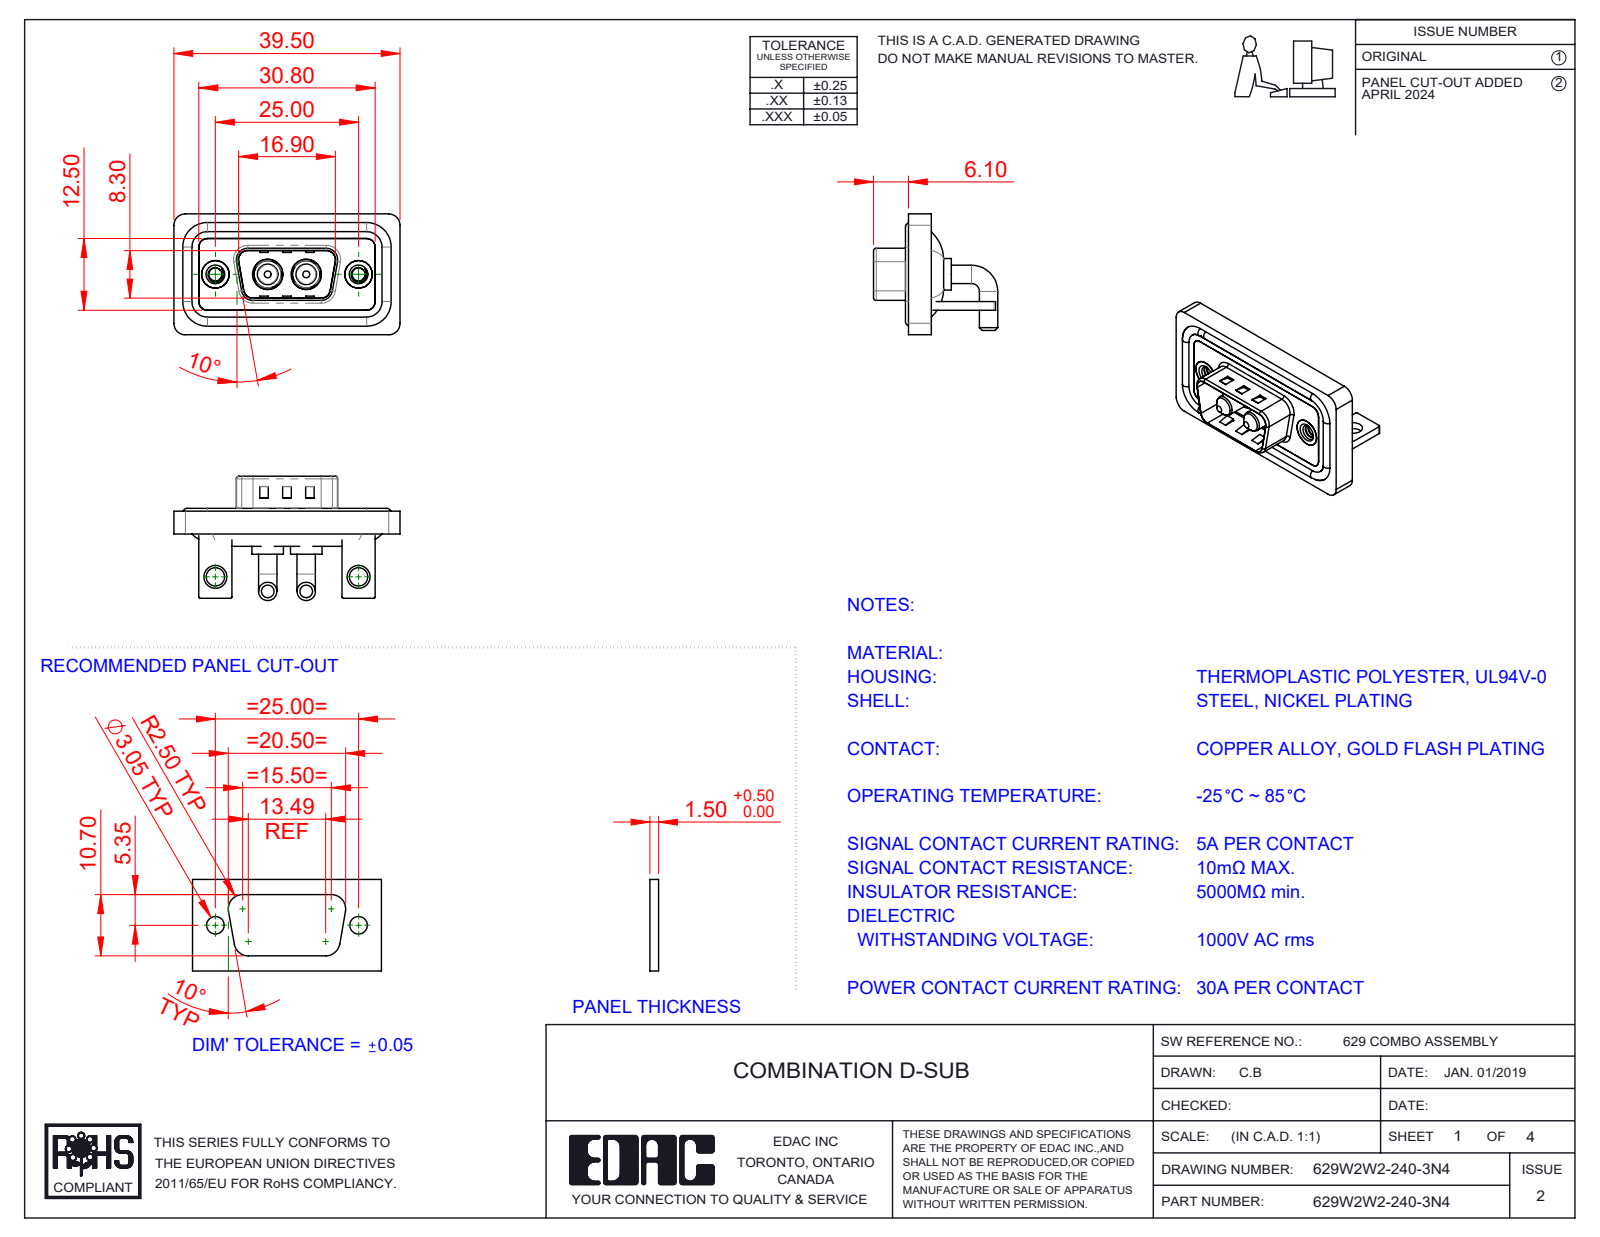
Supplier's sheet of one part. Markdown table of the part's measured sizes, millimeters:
| quantity | value |
| --- | --- |
| part name | 629W2W2-140-3N4; 629Combo Housing_2W2; 629Combo Shell Front_09 Contacts; 629Combo Stabilizer Bracket (+4 more) |
| STEP written by | SolidWorks 2023 (CONFIG_CONTROL_DESIGN) |
| units | millimeters |
| bodies | 13 solids, 537 faces (185 planar, 240 cylindrical, 112 other) |
| overall size | 39.5 × 21.7 × 21.1 |
| volume | 4 918 mm³ |
| surface area | 7 791 mm² |
| round holes (diameter × count) | 2.26 × 2, 3.2 × 2, 4 × 2, 4.8 × 2, 4.85 × 2, 5 × 2, 5.3 × 2 |
| round bosses / shafts (diameter × count) | 3.2 × 4, 1.6 × 4, 5.5 × 2, 5.2 × 2, 4.9 × 2, 4.75 × 2, 3.75 × 2, 3.6 × 2 |
| partial cylindrical surfaces (radius × count) | 2 × 19, 1.5 × 18, 0.25 × 16, 0.5 × 9, 1.6 × 8, 0.6 × 4, 0.65 × 4, 0.9 × 4 |
| main face-to-face distances | 0.4, 1.5, 2.9, 0.8, 1.1, 1.2, 2.1, 1.6, 3.7, 2.5 |
| hole center spacings | 9.14, 15.86, 25, 6.72 |
